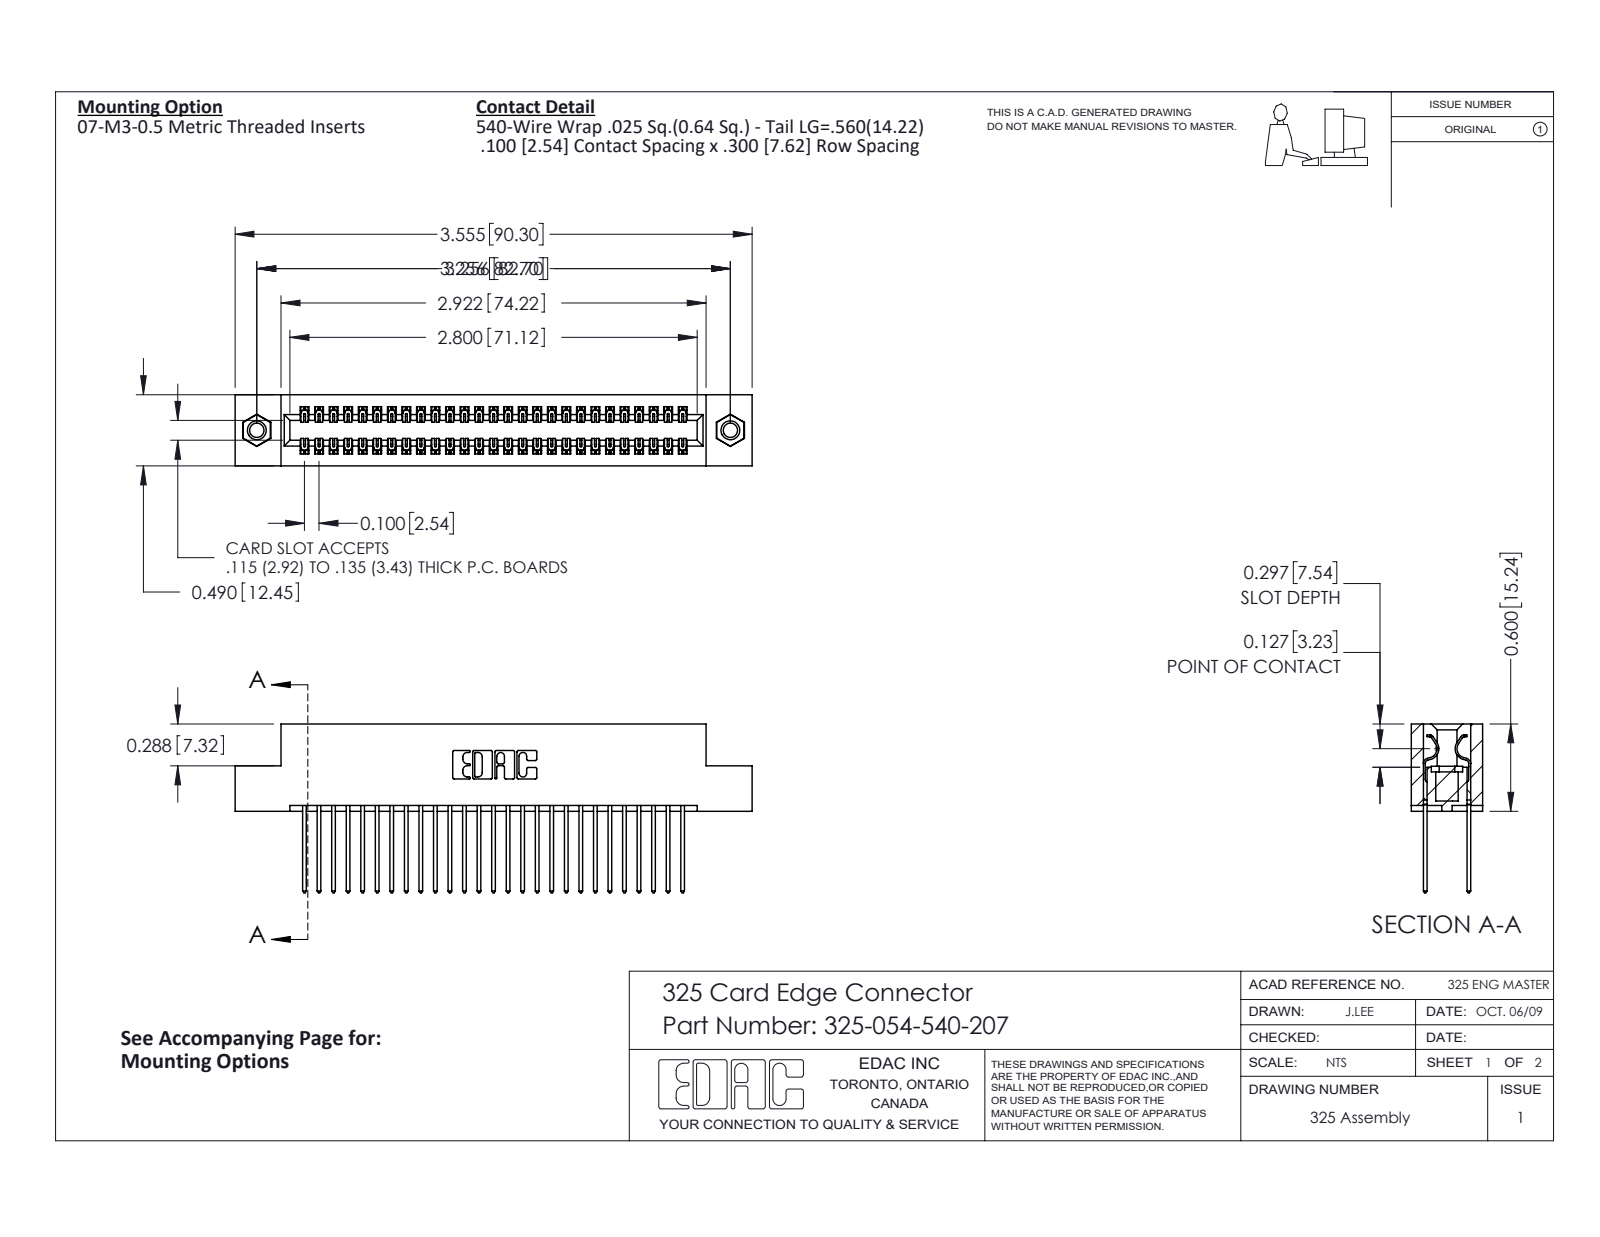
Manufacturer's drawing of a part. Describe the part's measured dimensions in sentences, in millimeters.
The part is named "325 Part_TI; 345-250-001_345-250-005-103; 325-054-540-207; 325-292-001_325-293-140". Its 3-D file was written by "SolidWorks 2016 (CONFIG_CONTROL_DESIGN)". It is 57 solids with 2982 faces: 2046 planar, 920 cylindrical and 16 other. Overall it measures 90.3 by 29.5 by 12.4 millimeters. Its volume is 11 700 cubic millimeters and its surface area 14 830 square millimeters. Round holes: 2 of diameter 2.5, 2 of diameter 3.2, 2 of diameter 4.1. Round bosses or shafts: 2 of diameter 3.9. Partial cylindrical surfaces (rounded edges, fillets, slot ends): 81 of radius 0.2, 54 of radius 0.3, 22 of radius 0.3, 6 of radius 0.2, 6 of radius 0.8, 3 of radius 0.7, 2 of radius 0.4, 2 of radius 0.6. The main face-to-face distances are 2.1, 10.3, 7.6, 2.7, 9.7, 0.6, 12.4, 8.3, 7, 1. The hole center spacings are 82.7.
